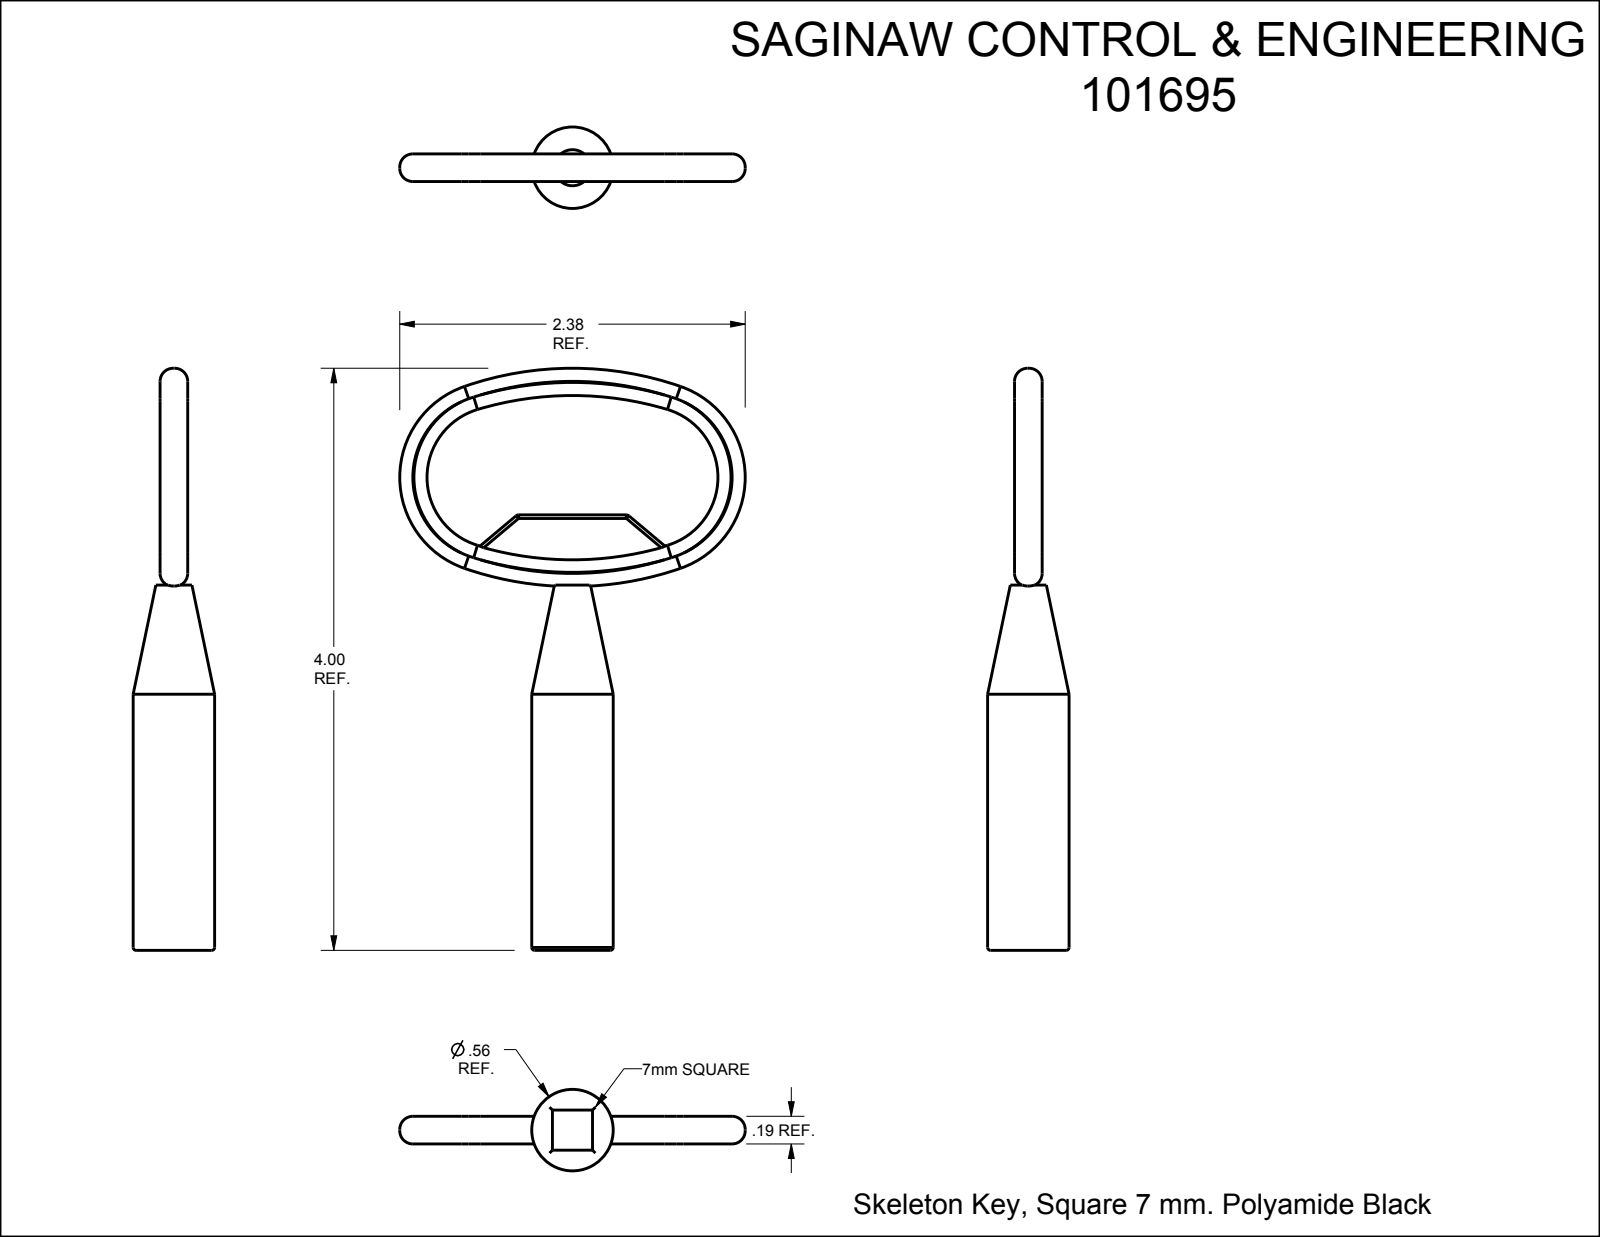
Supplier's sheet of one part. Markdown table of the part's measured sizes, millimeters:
| quantity | value |
| --- | --- |
| part name | 101695 |
| STEP written by | SolidWorks 2019 (AUTOMOTIVE_DESIGN) |
| units | millimeters |
| bodies | 1 solid, 69 faces (21 planar, 24 cylindrical, 24 other) |
| overall size | 101.6 × 60.3 × 14.2 |
| volume | 10 700 mm³ |
| surface area | 5 869 mm² |
| round bosses / shafts (diameter × count) | 14.2 × 1 |
| partial cylindrical surfaces (radius × count) | 0.6 × 6, 0.5 × 4, 57.6 × 4, 0.8 × 2, 12.4 × 2, 16.8 × 2 |
| main face-to-face distances | 7, 1.6, 4.3, 2.7, 2.7, 4.3, 19.1, 1.6, 3.2, 63.8 |
